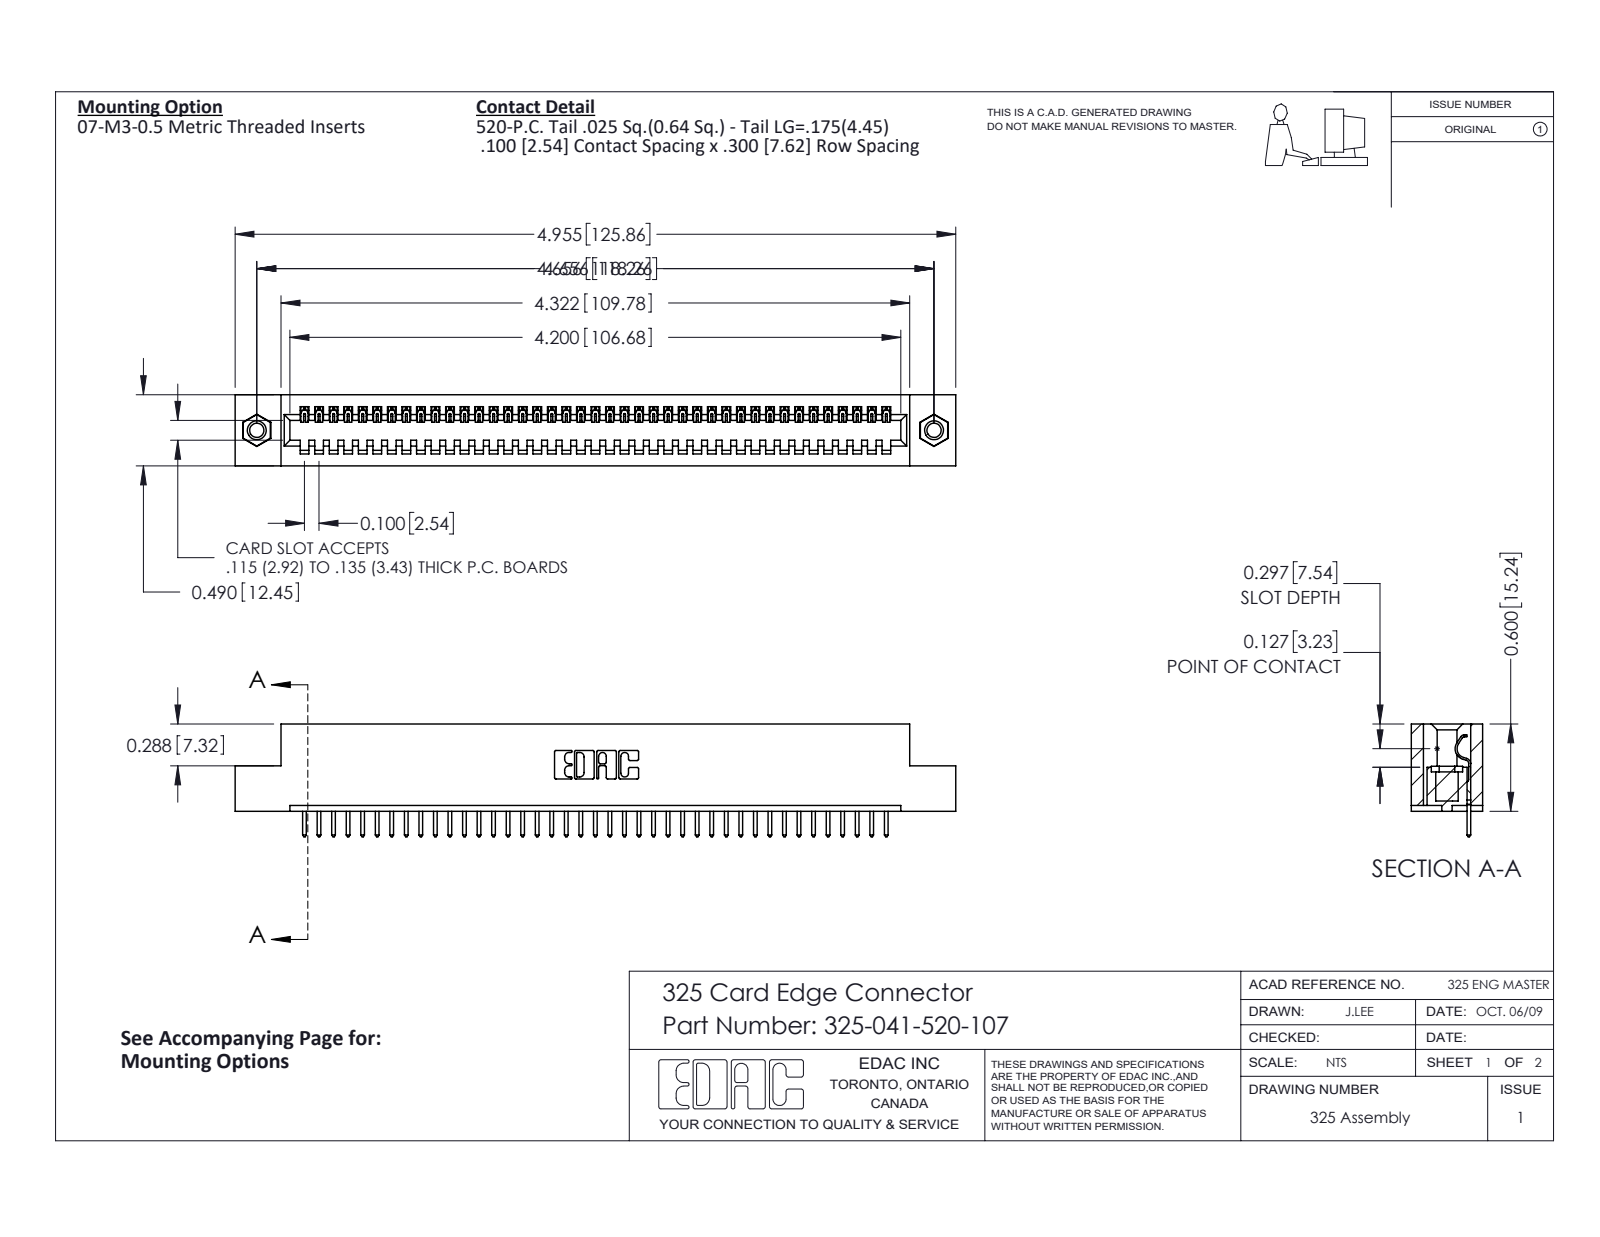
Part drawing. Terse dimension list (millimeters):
name: 325-041-520-107; 325-292-001_325-293-120; 345-250-001_345-250-005-103; 325 Part_TI
written by: SolidWorks 2016 (CONFIG_CONTROL_DESIGN)
unit: mm
bodies: 44 solids, 2552 faces (1824 planar, 712 cylindrical, 16 other)
size: 125.9 × 19.7 × 12.4
volume: 15 800 mm³; area: 16 900 mm²
holes: 2× ⌀2.5, 2× ⌀3.2, 2× ⌀4.1
bosses: 2× ⌀3.9
rounds: 82× R0.2, 82× R0.3, 22× R0.3, 6× R0.2, 6× R0.8, 3× R0.7, 1× R0.4, 1× R0.6
face distances: 2.1, 10.3, 12.4, 7.6, 2.7, 9.7, 0.6, 8.3, 14.2, 6.7
hole spacings: 118.3
